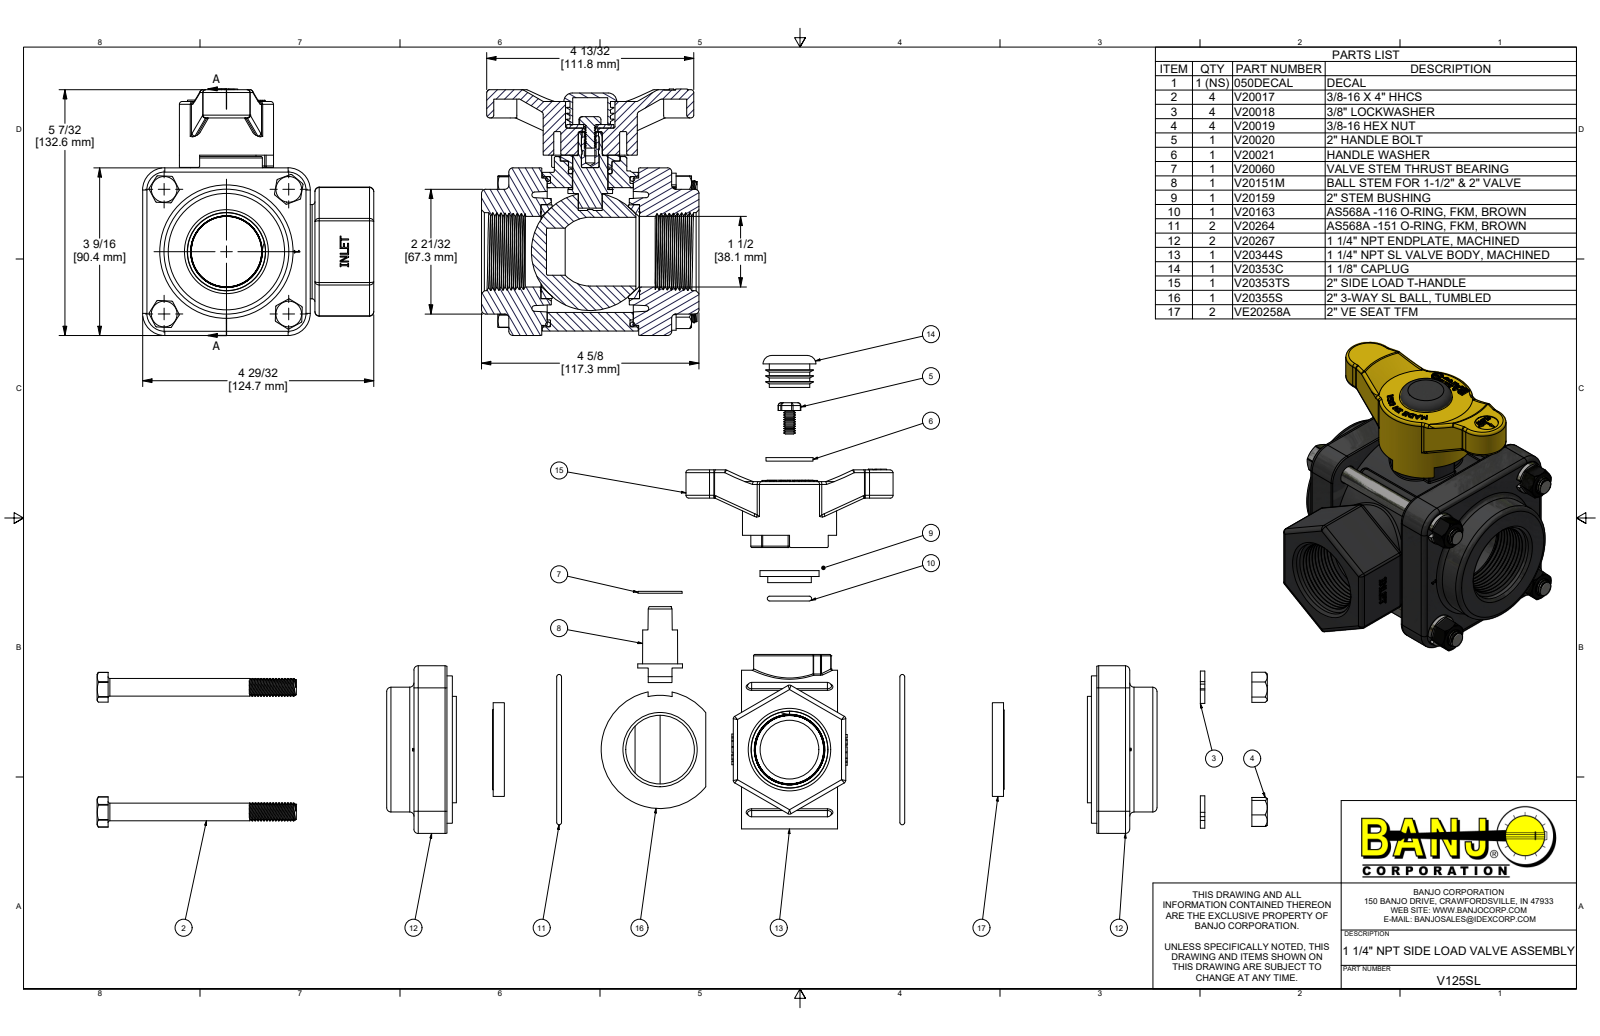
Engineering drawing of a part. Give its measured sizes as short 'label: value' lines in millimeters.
name: V125SL; V20344S; V20344SX; V20017 (+8 more)
written by: Autodesk Inventor 2022 (AUTOMOTIVE_DESIGN)
unit: mm
bodies: 29 solids, 2167 faces (815 planar, 537 cylindrical, 815 other)
size: 133 × 124.7 × 117.3
volume: 681 000 mm³; area: 200 800 mm²
holes: 4× ⌀7.8, 4× ⌀9.8, 4× ⌀10.3, 2× ⌀37.1, 1× ⌀4.4, 1× ⌀5, 1× ⌀6.2, 1× ⌀7.1, 1× ⌀8.1, 1× ⌀8.9, 1× ⌀9.5, 1× ⌀12.7
bosses: 60× ⌀8.2, 4× ⌀17.4, 4× ⌀9.5, 2× ⌀50.8, 1× ⌀79.5, 1× ⌀73.7, 1× ⌀67.3, 1× ⌀57.4
rounds: 52× R0.8, 44× R1.5, 30× R2.3, 8× R1.9, 8× R4.1, 4× R2.4, 4× R3.2, 4× R8.1
face distances: 17.8, 70.1, 20.7, 67.2, 2.9, 49.4, 90.4, 87.9, 32.5, 17.3
hole spacings: 47.5, 67.3, 95.1, 19.9, 46.4, 58
